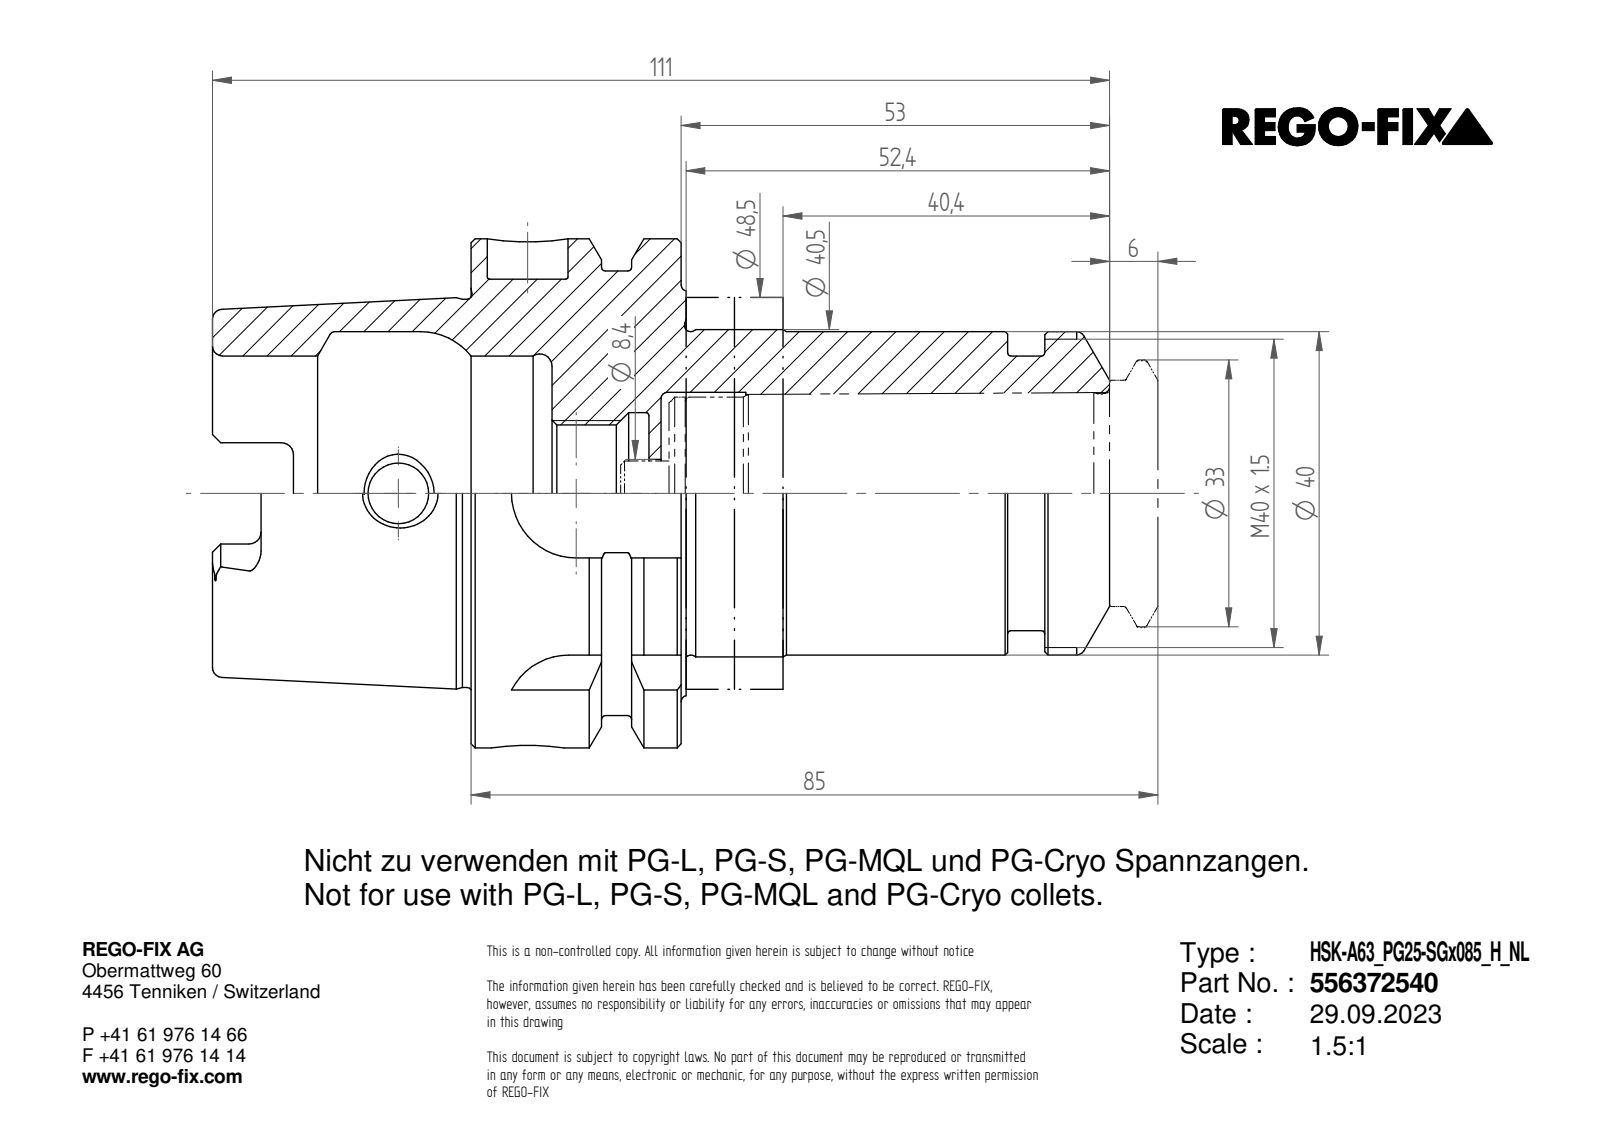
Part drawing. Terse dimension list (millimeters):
name: 0029445
written by: ST-DEVELOPER v16.7 (AUTOMOTIVE_DESIGN)
unit: mm
bodies: 2 solids, 167 faces (54 planar, 42 cylindrical, 71 other)
size: 117 × 63 × 63
volume: 149 525 mm³; area: 39 779 mm²
holes: 1× ⌀7.5, 1× ⌀8.4, 1× ⌀9, 1× ⌀10, 1× ⌀16.92, 1× ⌀20, 1× ⌀25, 1× ⌀34
bosses: 1× ⌀63, 1× ⌀55, 1× ⌀48.04, 1× ⌀40.5, 1× ⌀40, 1× ⌀33, 1× ⌀28, 1× ⌀24.7
rounds: 6× R1.5, 4× R2.88, 4× R8
face distances: 26, 85, 59, 2.5, 10, 1.5, 16, 75, 26.6, 16.6
